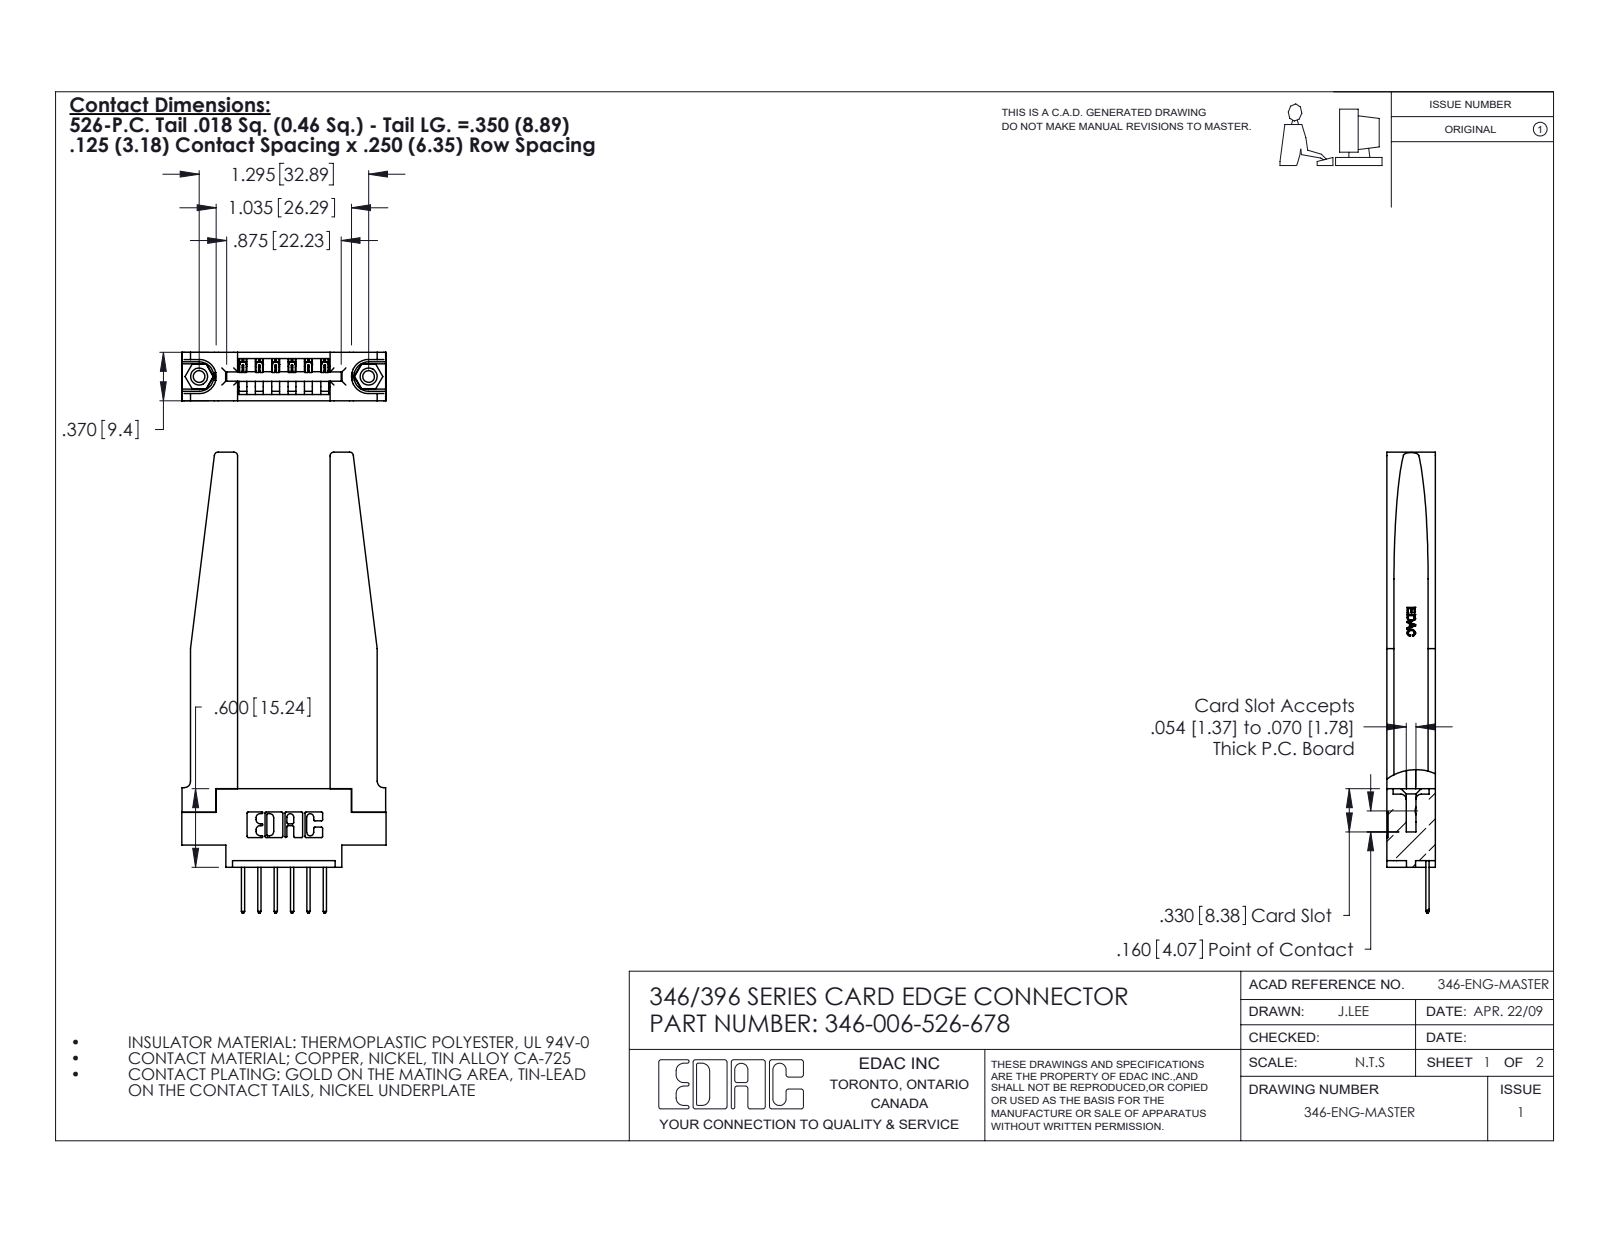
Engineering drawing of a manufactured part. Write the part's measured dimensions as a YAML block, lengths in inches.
part_name: "346 Part_0.170 Offset - 0.156 Dia-TH; 346-006-526-678; 346-220-078_345-220-078; 345-292-001_345-293-126 (+1 more)"
step_written_by: "SolidWorks 2020 (CONFIG_CONTROL_DESIGN)"
units: inches
bodies: {solids: 11, faces: 722, planar: 476, cylindrical: 194, other: 52}
overall_size: [3.52, 1.56, 0.37]
volume: 0.627
surface_area: 16.35
round_holes:
  - {diameter: 0.089, count: 2}
  - {diameter: 0.125, count: 2}
  - {diameter: 0.156, count: 2}
  - {diameter: 0.064, count: 1}
round_bosses_or_shafts:
  - {diameter: 0.155, count: 2}
partial_cylinders:
  - {radius: 0.01, count: 22}
  - {radius: 0.006, count: 12}
  - {radius: 0.01, count: 12}
  - {radius: 0.03, count: 8}
  - {radius: 0.007, count: 6}
  - {radius: 0.031, count: 6}
  - {radius: 0.026, count: 3}
  - {radius: 0.031, count: 2}
face_to_face_distances: [0.37, 0.15, 0.22, 0.25, 0.706, 0.072, 0.148, 0.048, 0.322, 0.102]
hole_center_spacings: [0.246, 1.092, 1.295]
